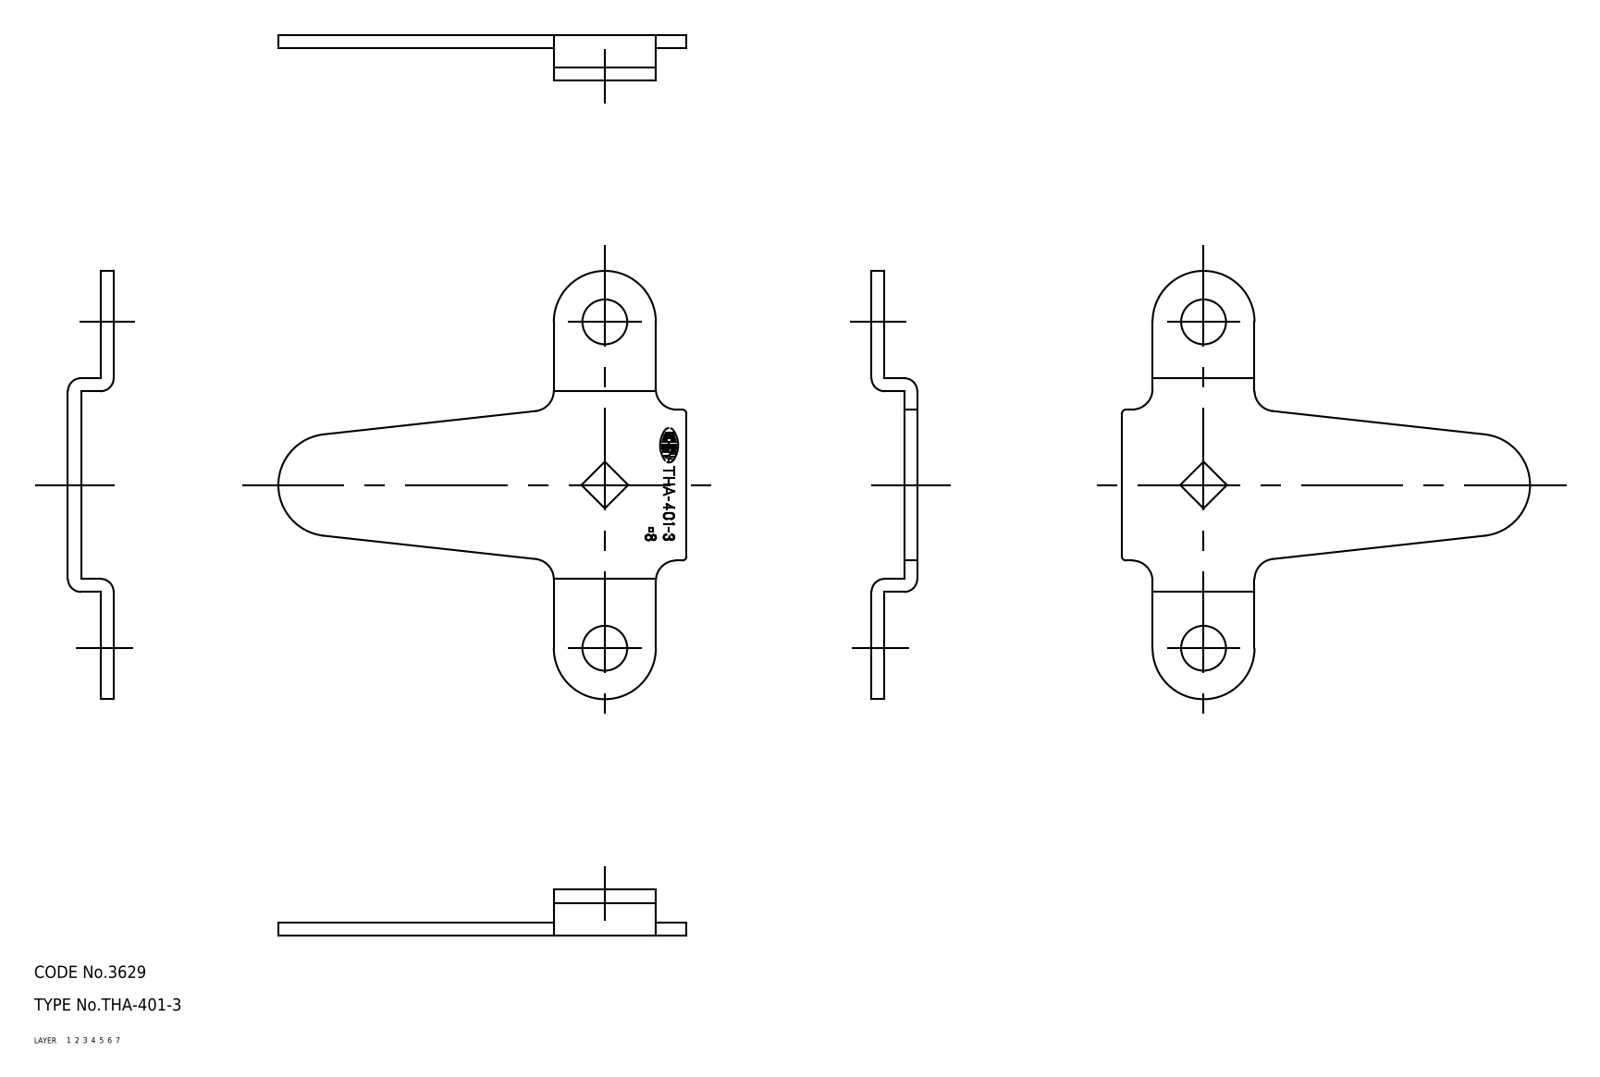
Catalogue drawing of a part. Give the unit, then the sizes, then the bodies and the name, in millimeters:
Units: millimetres
Overall size (bounding box): 105 × 100 × 11.2
Volume: 15 436 mm³ · Surface area: 11 203 mm²
Bodies: 1 solid, 40 faces (0 planar, 0 cylindrical, 40 other)
Part name (STEP PRODUCT): cam
STEP written by: CADfix (AUTOMOTIVE_DESIGN)
